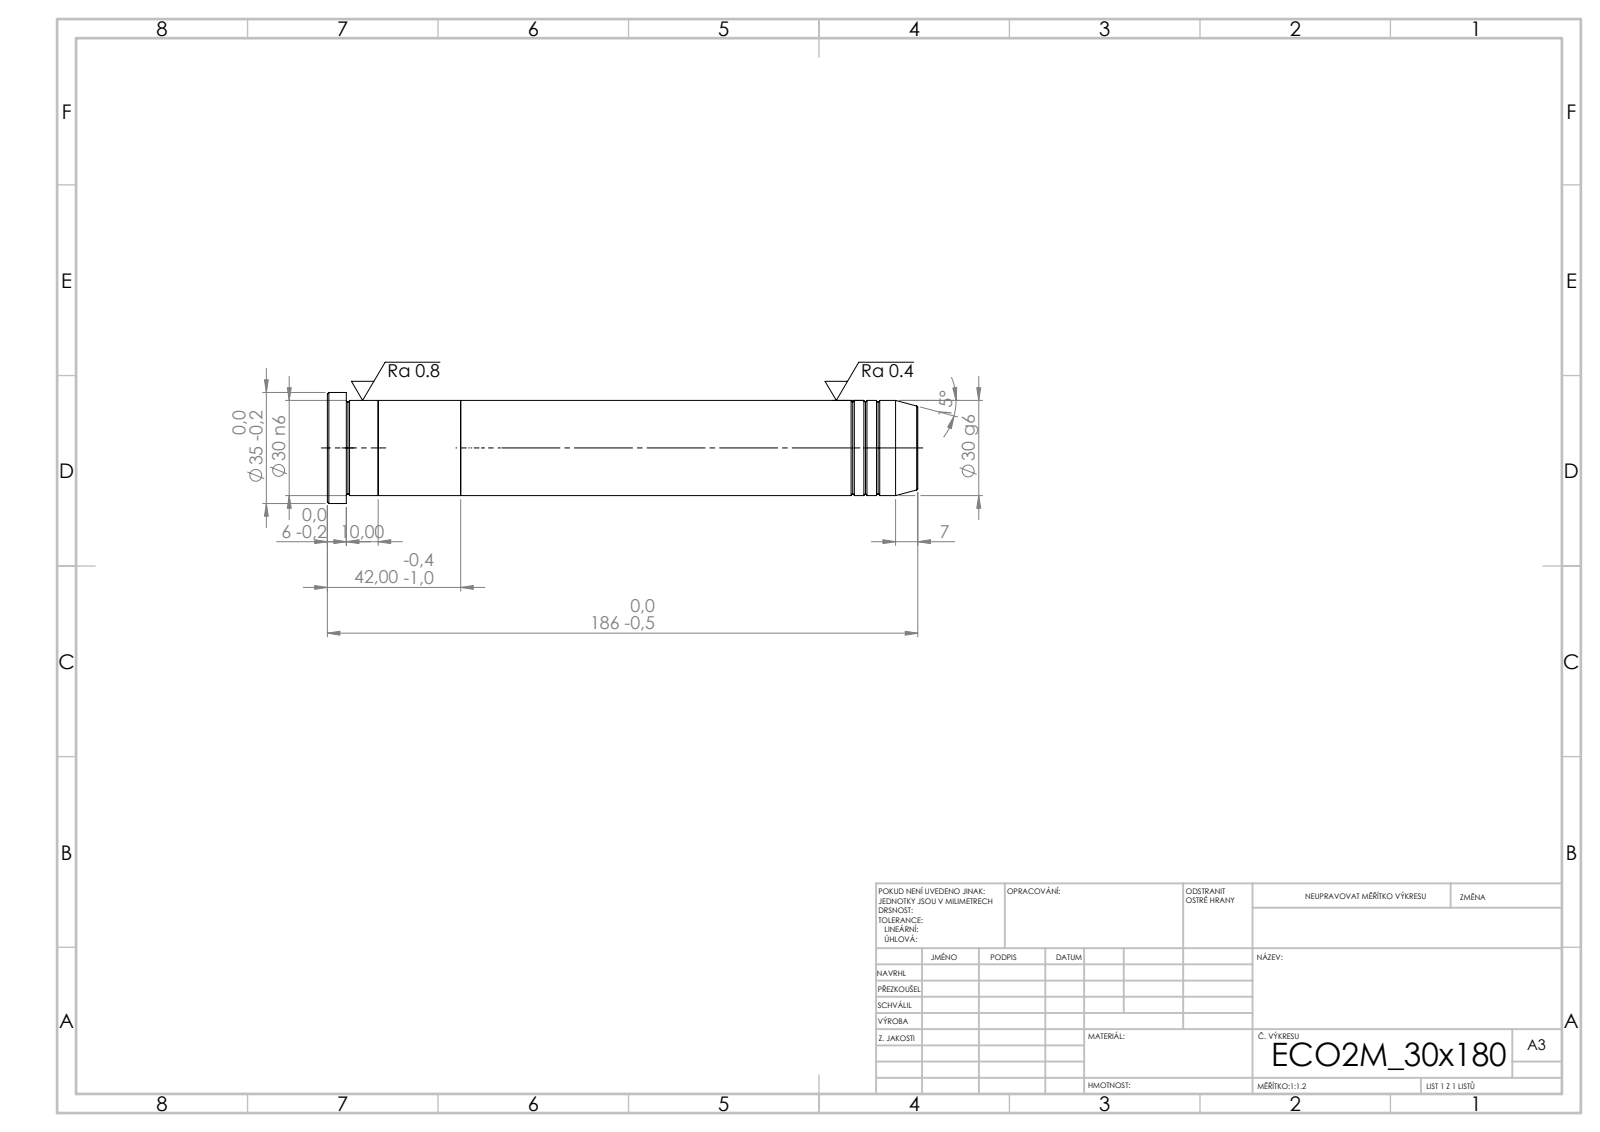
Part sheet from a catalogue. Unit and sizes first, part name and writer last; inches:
Units: inches
Overall size (bounding box): 7.323 × 1.378 × 1.378
Round bosses / shafts (diameter × count): ⌀1.378 ×1, ⌀1.181 ×1
Main face-to-face distances: 1.024, 1.654, 0.63, 5.669, 6.693, 7.323, 7.087, 1.417, 0.394, 0.236
Volume: 8.071 in³ · Surface area: 34.65 in²
Bodies: 3 solids, 43 faces (7 planar, 14 cylindrical, 22 other)
STEP written by: SolidWorks 2019 (CONFIG_CONTROL_DESIGN)
